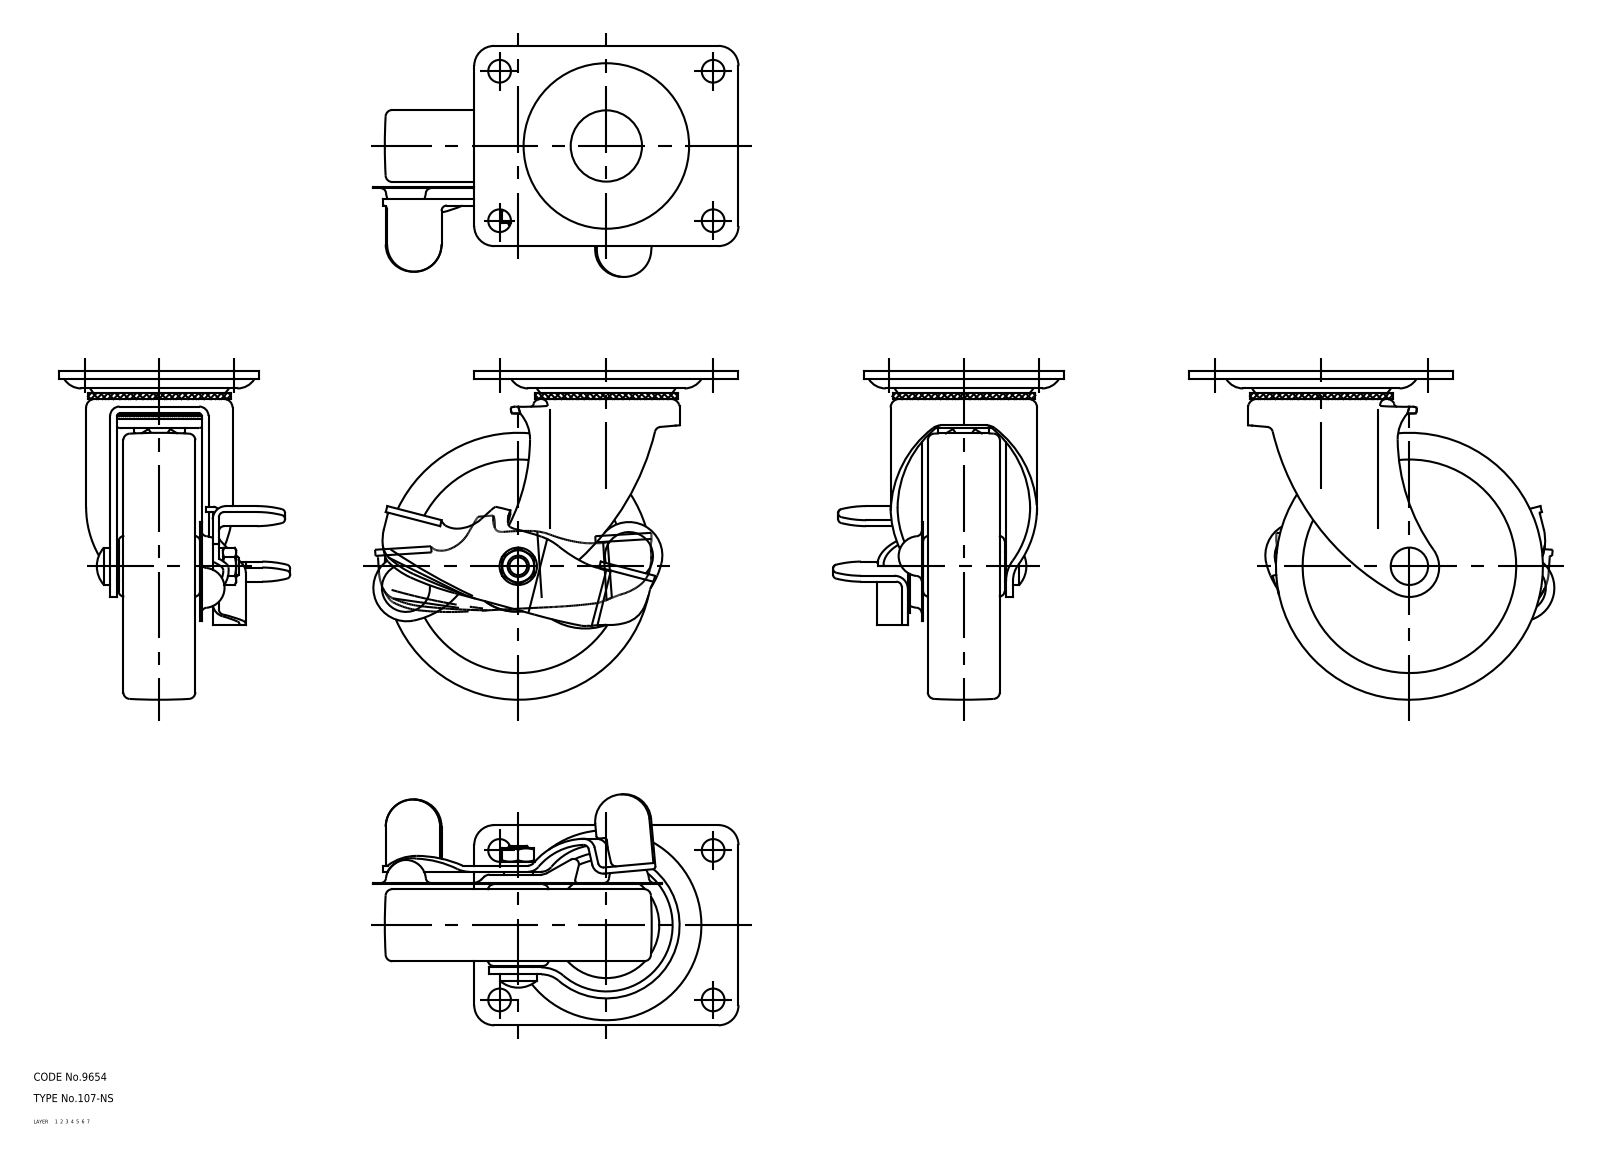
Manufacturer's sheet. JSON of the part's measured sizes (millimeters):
{"part_name": "wheel; plate; mounting plate; main shaft (+3 more)", "step_written_by": "CADfix (AUTOMOTIVE_DESIGN)", "units": "millimeters", "bodies": {"solids": 7, "faces": 368, "planar": 0, "cylindrical": 0, "other": 368}, "overall_size": [136.79, 123, 86.62], "volume_mm3": 217553, "surface_area_mm2": 85350}
